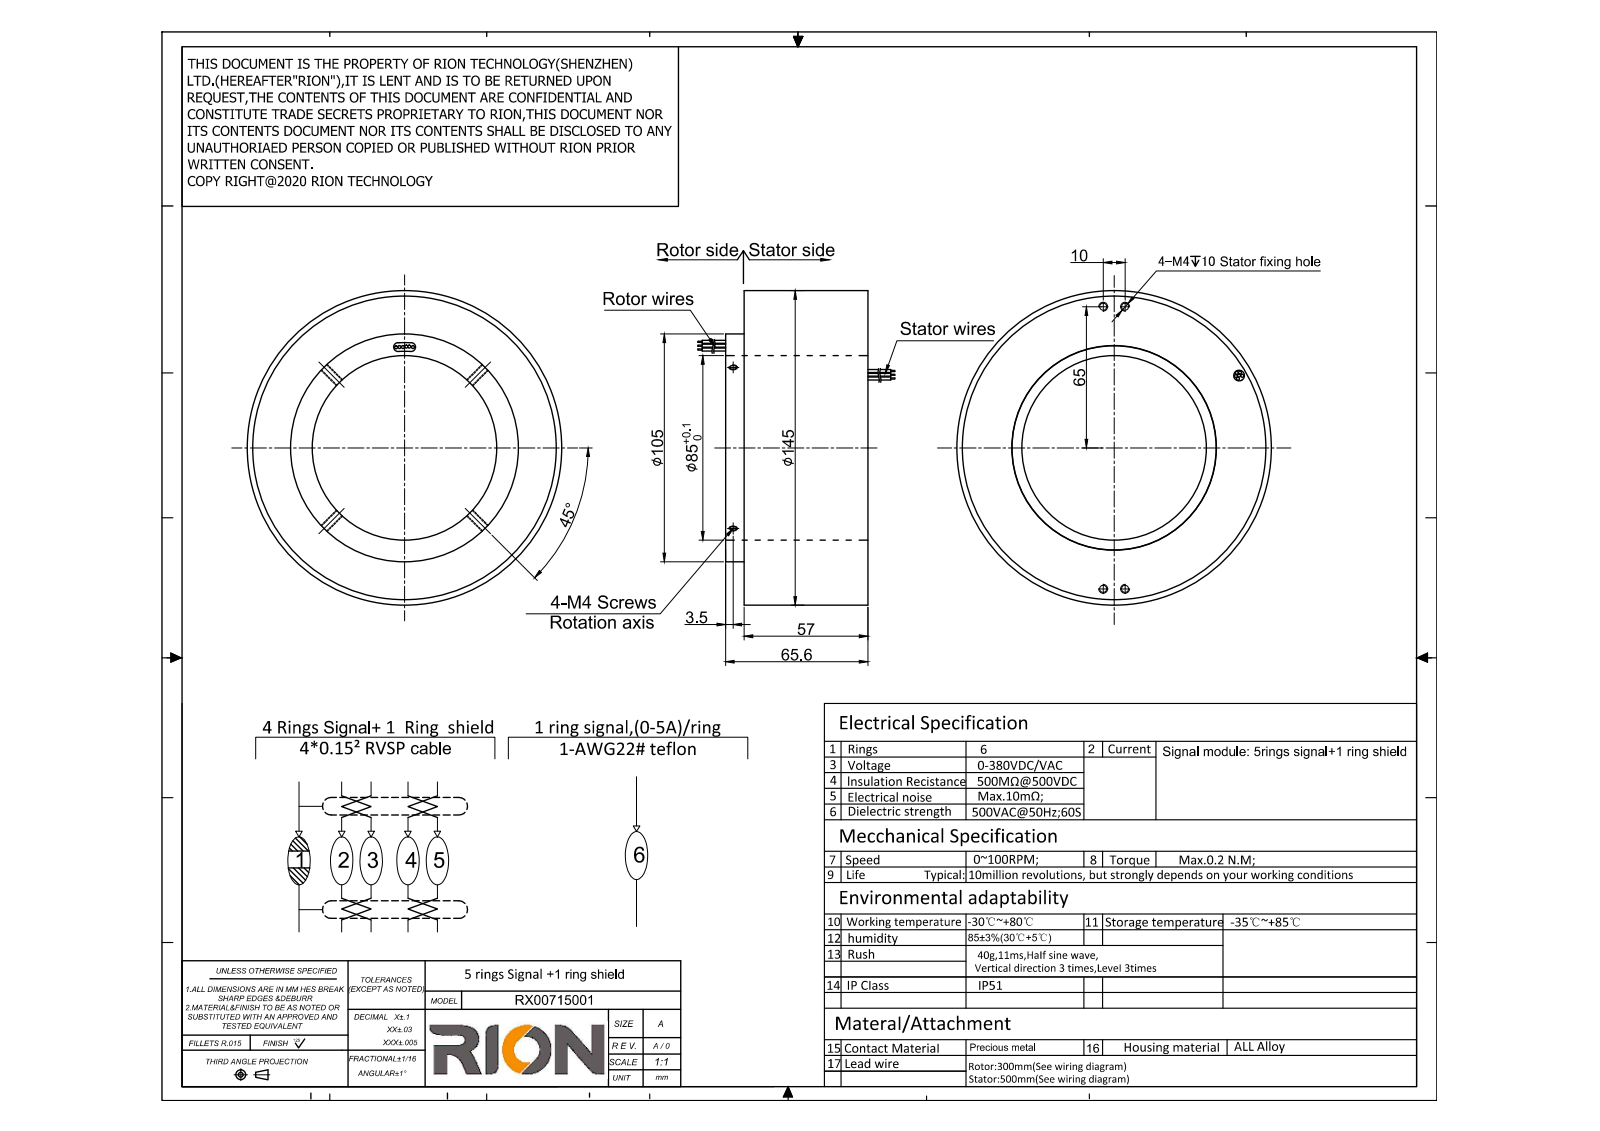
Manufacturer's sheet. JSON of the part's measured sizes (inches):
{"part_name": "RX00715001", "step_written_by": "SolidWorks 2014 (CONFIG_CONTROL_DESIGN)", "units": "inches", "bodies": {"solids": 1, "faces": 92, "planar": 27, "cylindrical": 65, "other": 0}, "overall_size": [5.709, 5.709, 3.213], "volume_in3": 39.2, "surface_area_in2": 113.6, "round_holes": [[0.157, 8], [0.197, 1], [3.346, 1], [3.705, 1], [5.516, 1]], "round_bosses_or_shafts": [[0.051, 12], [5.709, 1], [5.512, 1], [4.134, 1], [3.701, 1]], "partial_cylinders_radius": [[0.079, 2], [1.752, 1], [1.909, 1]], "face_to_face_distances": [2.244, 0.339, 2.583, 0.079, 0.394, 2.504, 2.189, 1.85, 2.165, 0.039], "hole_center_spacings": [2.567, 0.145, 0.394, 5.118, 5.133, 2.419, 2.618, 2.763]}
